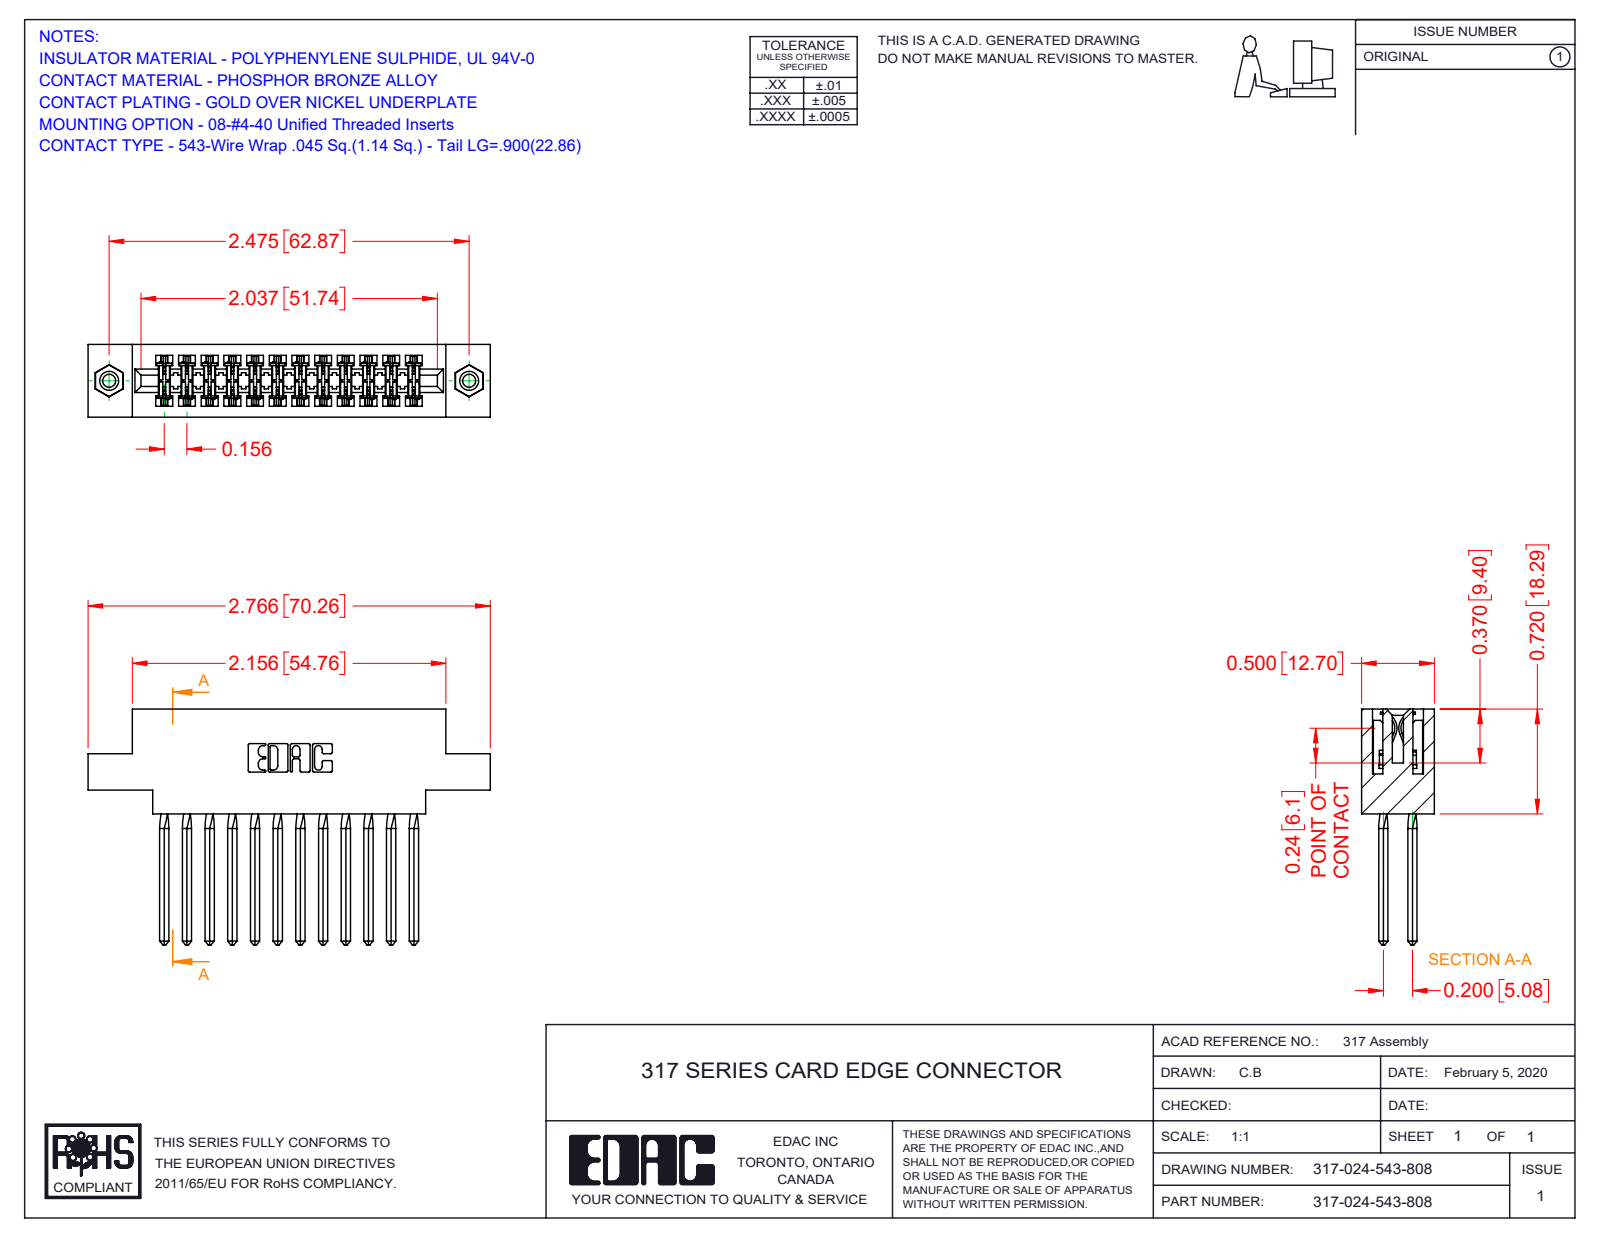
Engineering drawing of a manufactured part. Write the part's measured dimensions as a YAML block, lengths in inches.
part_name: "345-250-001_345-250-003-102; 317-024-543-808; 317-290-001_543; 317 Part_.156 Dia - TI"
step_written_by: "SolidWorks 2016 (CONFIG_CONTROL_DESIGN)"
units: inches
bodies: {solids: 27, faces: 2298, planar: 1842, cylindrical: 344, other: 112}
overall_size: [2.766, 1.62, 0.5]
volume: 0.665
surface_area: 23.82
round_holes:
  - {diameter: 0.089, count: 2}
  - {diameter: 0.125, count: 2}
  - {diameter: 0.156, count: 2}
round_bosses_or_shafts:
  - {diameter: 0.155, count: 2}
partial_cylinders:
  - {radius: 0.015, count: 48}
  - {radius: 0.01, count: 22}
  - {radius: 0.007, count: 6}
  - {radius: 0.031, count: 6}
  - {radius: 0.026, count: 3}
  - {radius: 0.095, count: 2}
  - {radius: 0.1, count: 2}
  - {radius: 0.11, count: 2}
face_to_face_distances: [0.5, 0.075, 0.425, 0.11, 0.22, 0.35, 0.331, 0.136, 0.156, 0.305]
hole_center_spacings: [2.475]
